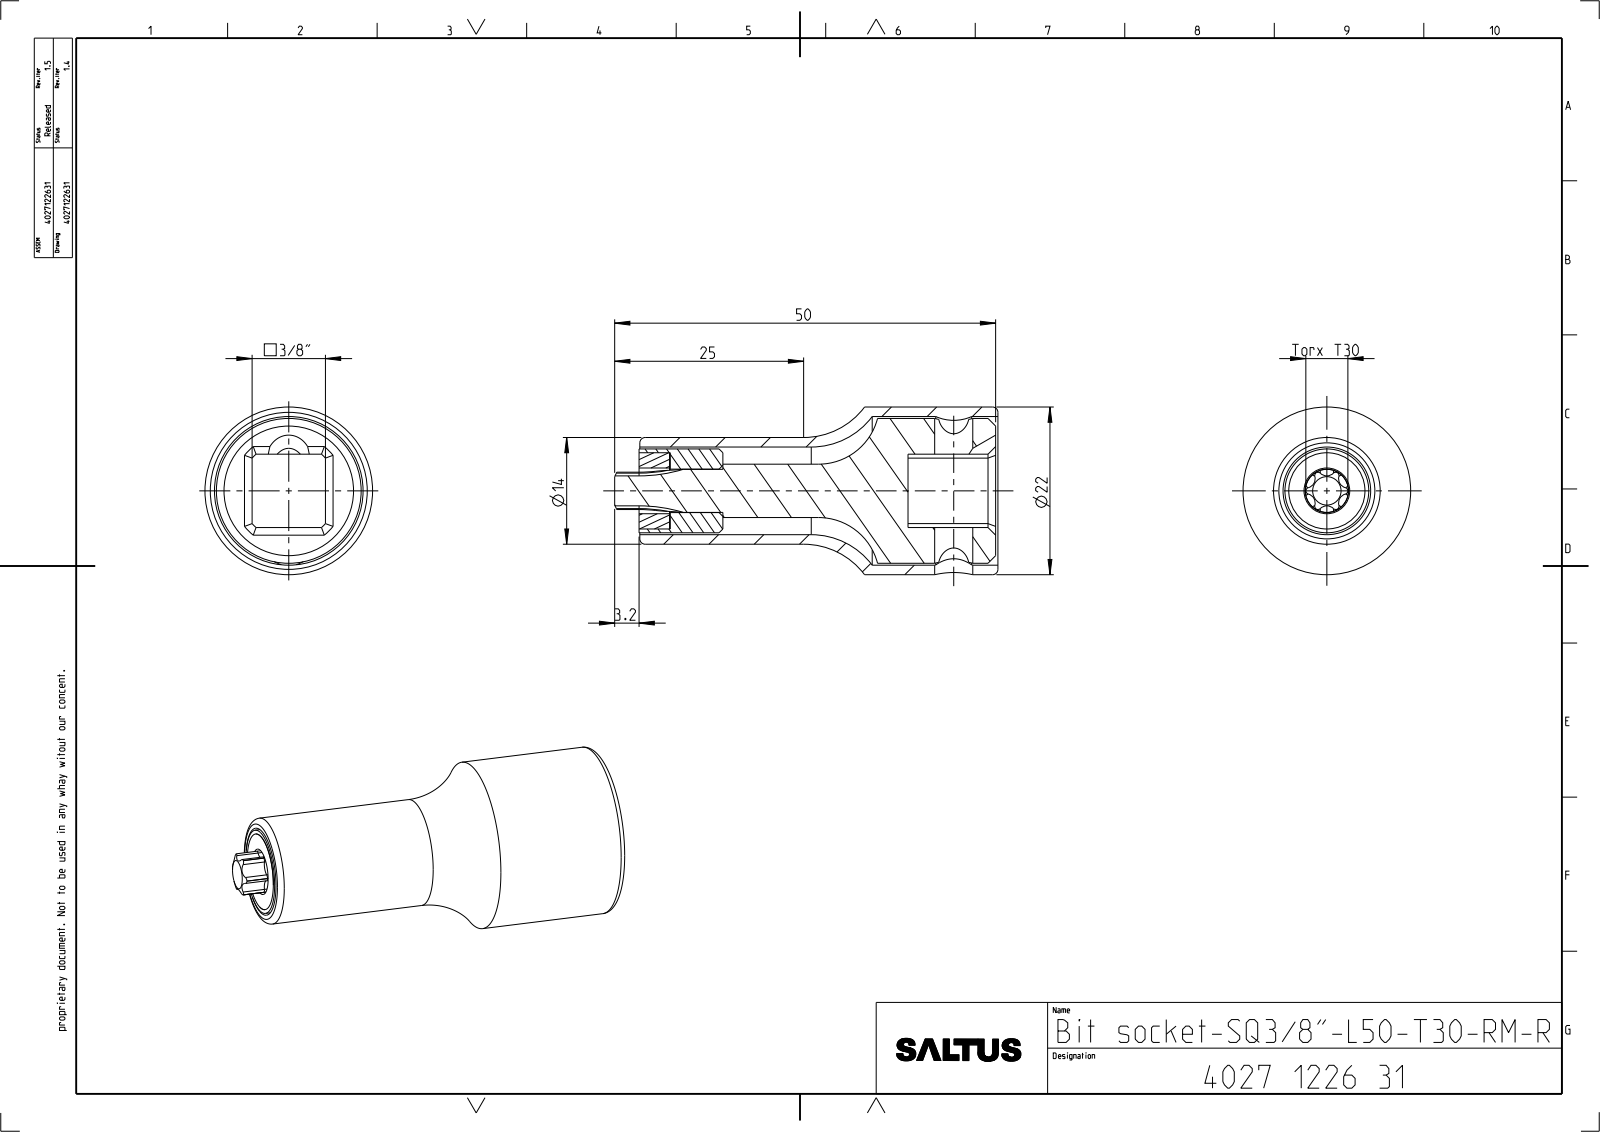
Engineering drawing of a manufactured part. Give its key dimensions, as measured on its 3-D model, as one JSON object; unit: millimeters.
{"part_name": "4027904044; 4027901681; 4027907728; 4027904020_ASM (+2 more)", "step_written_by": "CREO PARAMETRIC BY PTC INC, 2022414 (CONFIG_CONTROL_DESIGN)", "units": "millimeters", "bodies": {"solids": 4, "faces": 132, "planar": 20, "cylindrical": 63, "other": 49}, "overall_size": [50.3, 22, 22], "volume_mm3": 8299, "surface_area_mm2": 8620, "round_holes": [[5, 1], [5.7, 1], [6, 1], [10.1, 1], [11.5, 1], [19.5, 1]], "round_bosses_or_shafts": [[22, 1], [19, 1], [14, 1], [11, 1], [10, 1], [7, 1], [5.65, 1]], "partial_cylinders_radius": [[0.42, 12], [1.22, 6], [2.76, 1], [3, 1], [6.45, 1]], "face_to_face_distances": [9.62, 11.5, 4, 46.8, 35.3, 35.8, 24.3, 11, 42.7, 31.2]}
